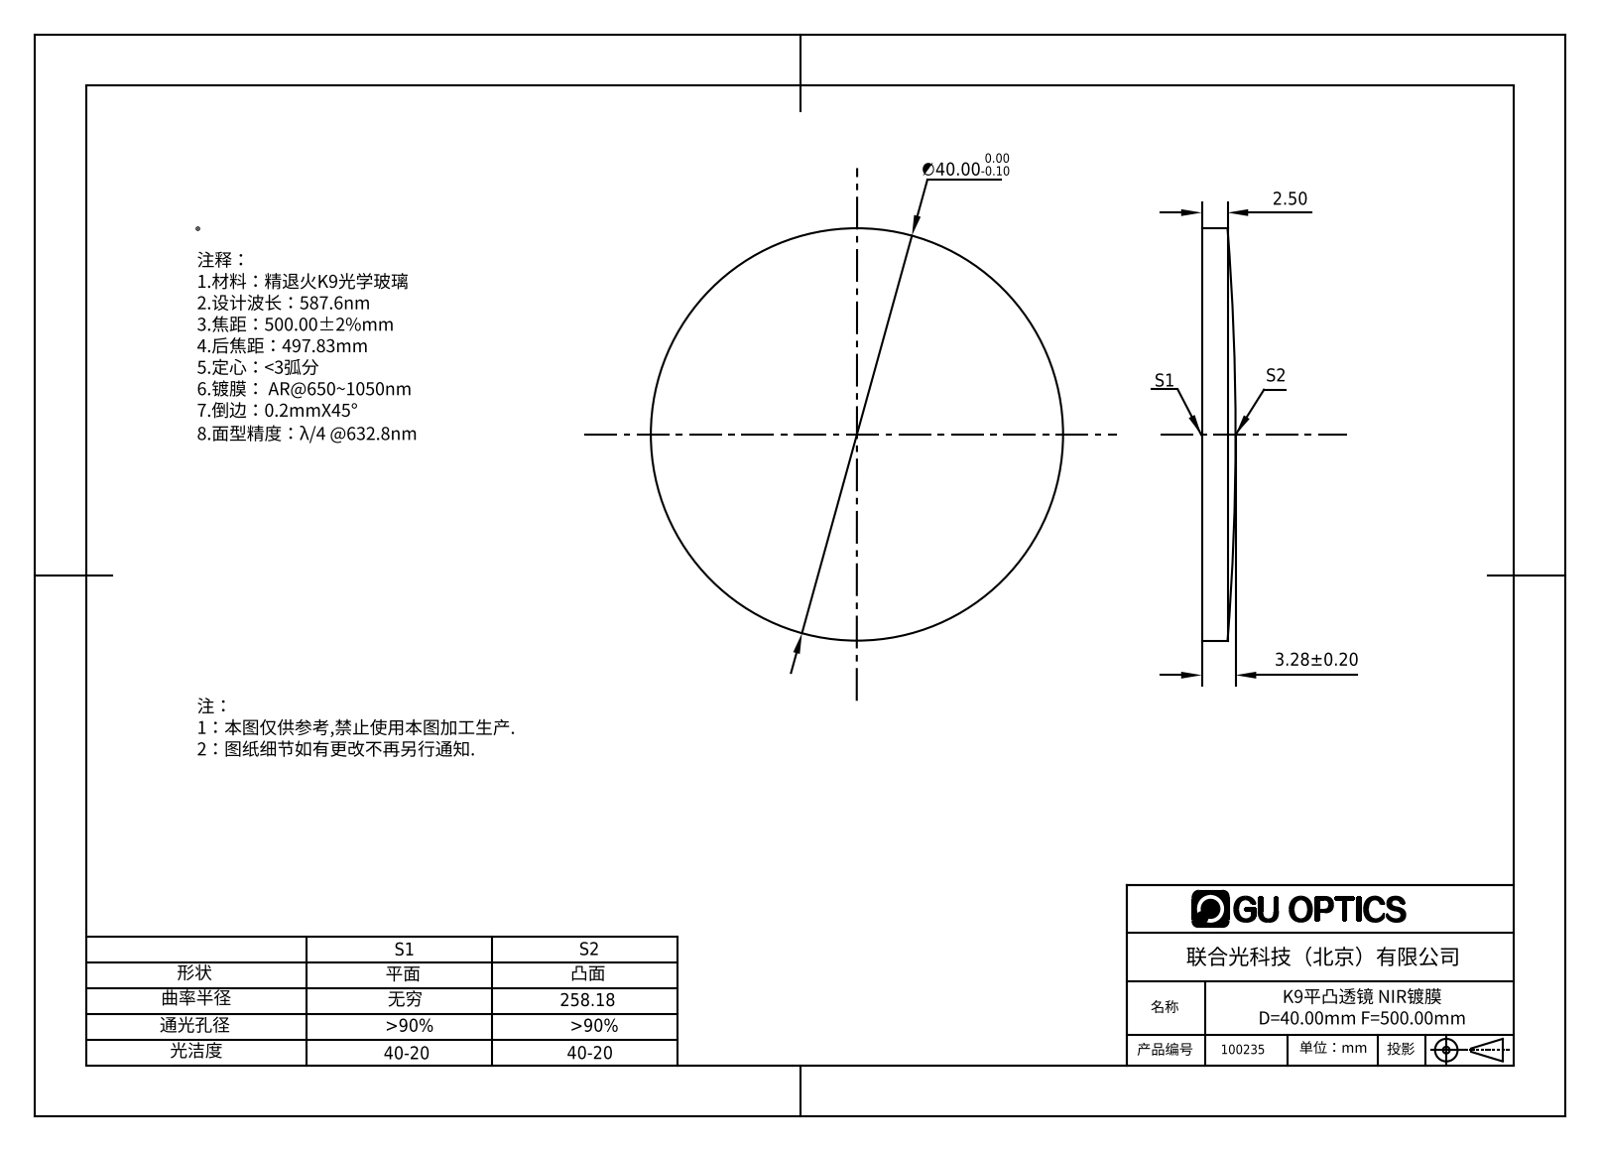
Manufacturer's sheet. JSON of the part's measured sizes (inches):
{"part_name": "100235", "step_written_by": "SolidWorks 2016 (AUTOMOTIVE_DESIGN)", "units": "inches", "bodies": {"solids": 1, "faces": 5, "planar": 1, "cylindrical": 2, "other": 2}, "overall_size": [1.575, 1.575, 0.129], "volume_in3": 0.222, "surface_area_in2": 4.385, "round_bosses_or_shafts": [[1.575, 1]]}
